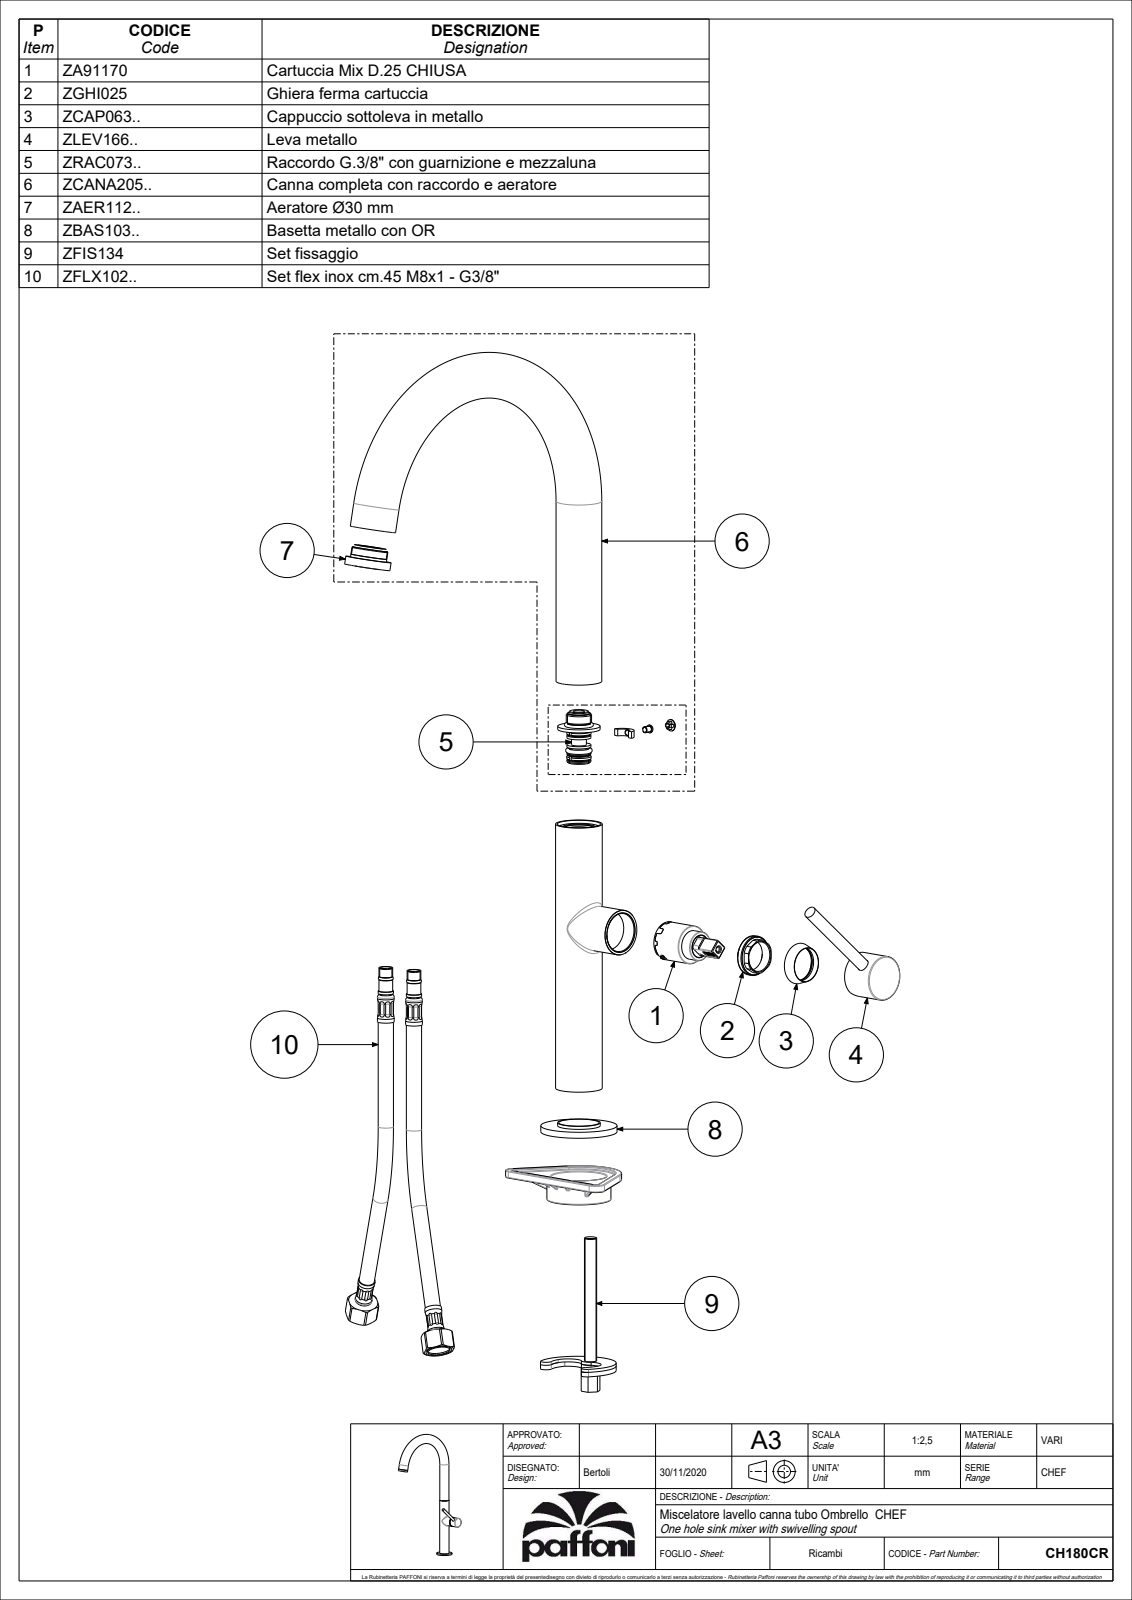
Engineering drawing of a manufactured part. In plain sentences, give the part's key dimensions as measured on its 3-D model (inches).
The part is named "CH180CR". Its 3-D file was written by "CREO PARAMETRIC BY PTC INC, 2020044 (CONFIG_CONTROL_DESIGN)". It is 7 solids with 1803 faces: 1512 planar, 170 cylindrical and 121 other. Overall it measures 16.15 by 9.127 by 3.485 inches. Its volume is 10.39 cubic inches and its surface area 200.5 square inches. Round holes: 6 of diameter 0.197, 2 of diameter 0.118, 2 of diameter 0.126, 2 of diameter 0.276, 2 of diameter 0.346, 2 of diameter 0.63, 2 of diameter 0.669, 2 of diameter 0.965, 2 of diameter 1.063, 1 of diameter 0.157, 1 of diameter 0.165, 1 of diameter 0.236. Round bosses or shafts: 2 of diameter 1.181, 2 of diameter 1.055, 2 of diameter 0.299, 2 of diameter 0.217, 1 of diameter 1.969, 1 of diameter 1.654, 1 of diameter 1.205, 1 of diameter 1.161. Partial cylindrical surfaces (rounded edges, fillets, slot ends): 9 of radius 0.02, 8 of radius 0.039, 2 of radius 0.079, 1 of radius 0.197. The main face-to-face distances are 0.157, 0.059, 0.394, 0.079, 0.098, 0.02, 0.118, 0.039, 0.209, 0.205. The hole center spacings are 0.25, 0.371, 0.414, 0.618, 0.167, 0.197, 0.205, 0.312.
